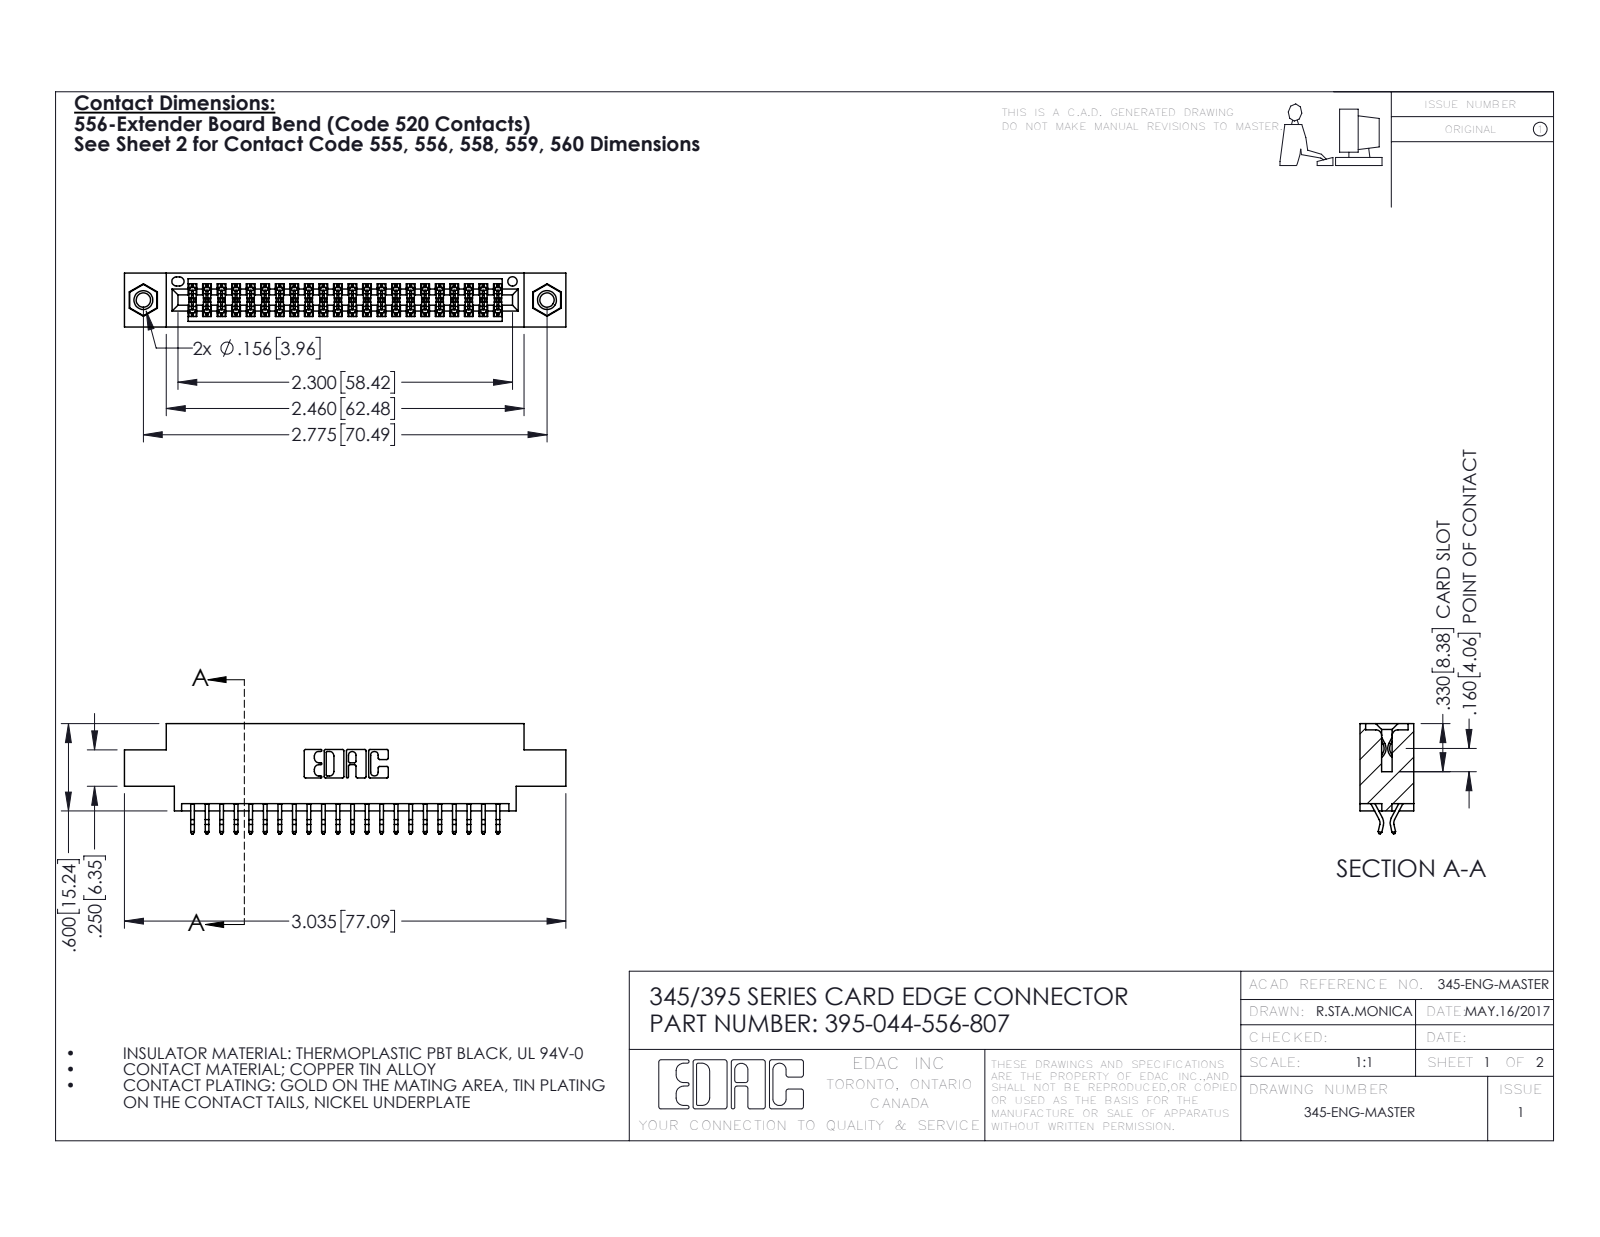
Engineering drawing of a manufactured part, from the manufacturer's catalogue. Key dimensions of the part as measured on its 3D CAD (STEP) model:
Part name (STEP PRODUCT): 395-044-556-807; 345 Part_0.170 Offset - 0.156 Dia-TI; 345-250-001_345-250-005-103; 345-292-001_556 Tail
STEP written by: SolidWorks 2016 (CONFIG_CONTROL_DESIGN)
Units: inches
Bodies: 47 solids, 2654 faces (1744 planar, 894 cylindrical, 16 other)
Overall size (bounding box): 3.035 × 0.757 × 0.37
Volume: 0.438 in³ · Surface area: 16.04 in²
Round holes (diameter × count): ⌀0.098 ×2, ⌀0.125 ×2, ⌀0.156 ×2, ⌀0.064 ×1
Round bosses / shafts (diameter × count): ⌀0.155 ×2
Partial cylindrical surfaces — rounded edges, fillets, slot ends (radius × count): R0.006 ×66, R0.01 ×22, R0.007 ×6, R0.031 ×6, R0.026 ×3, R0.01 ×2, R0.014 ×2, R0.019 ×2
Main face-to-face distances: 0.072, 0.298, 0.37, 0.2, 0.025, 0.098, 0.272, 0.225, 0.175, 0.149
Hole centre spacings: 0.27, 2.541, 2.775
